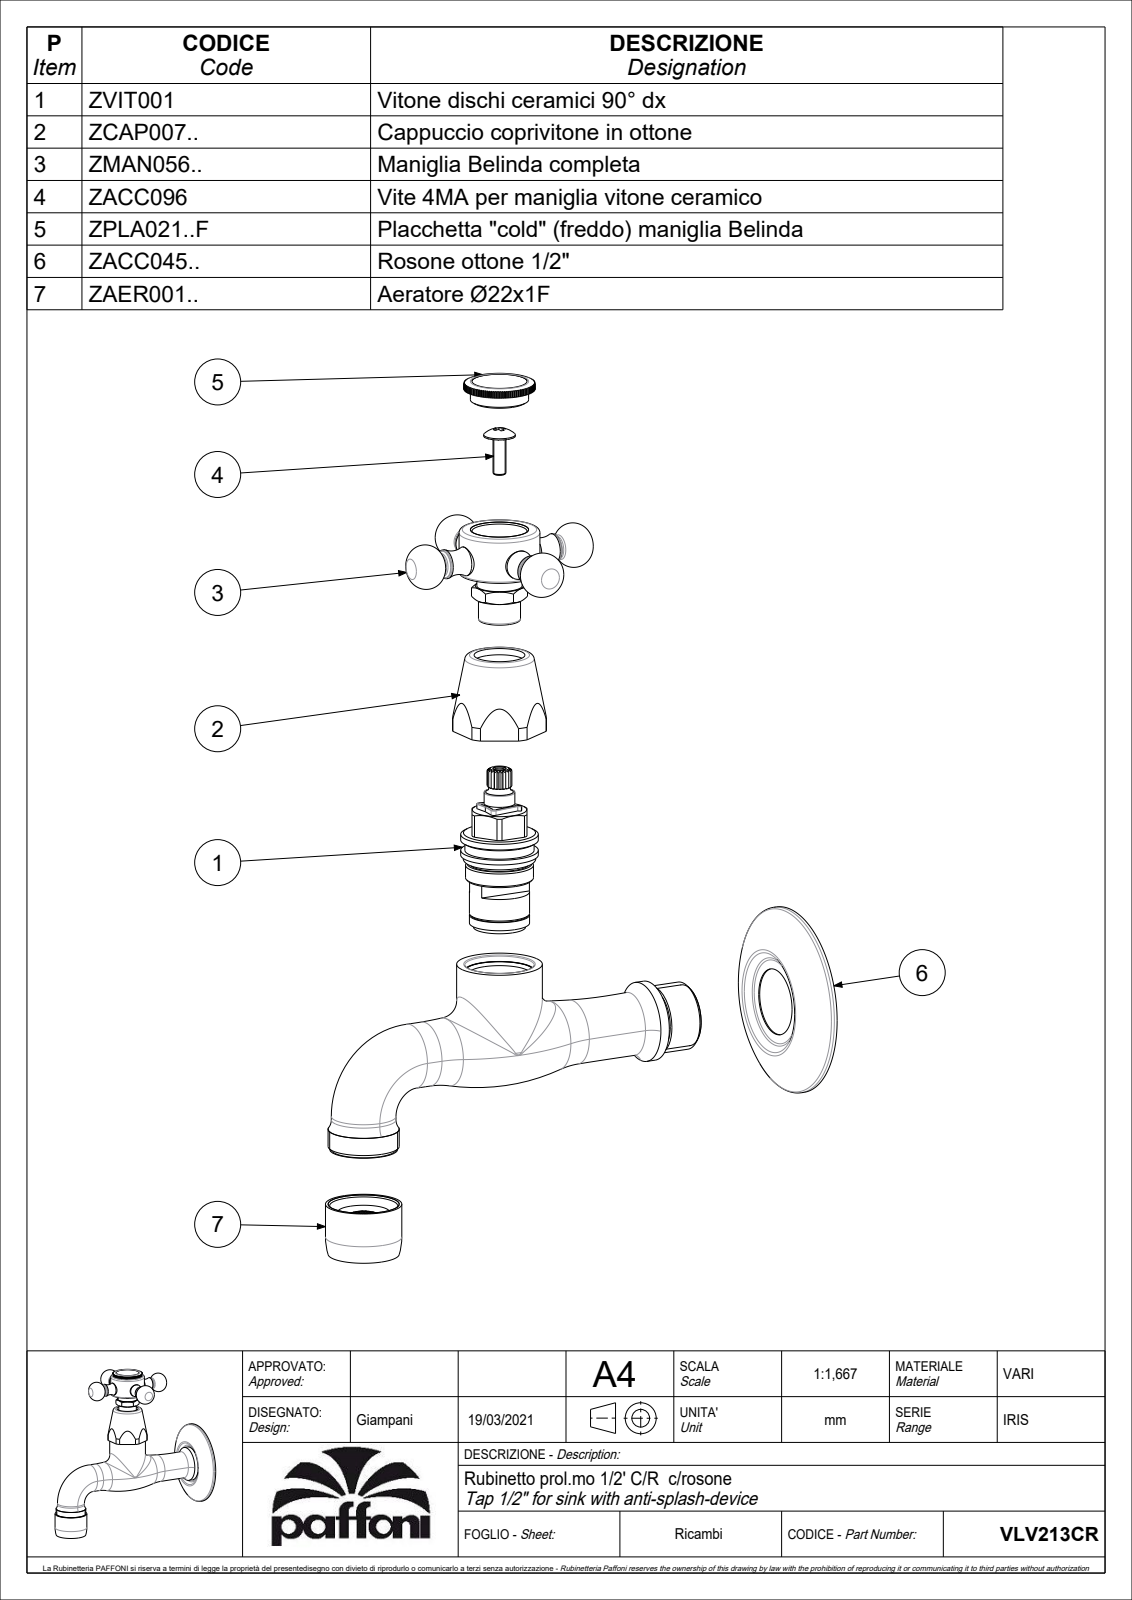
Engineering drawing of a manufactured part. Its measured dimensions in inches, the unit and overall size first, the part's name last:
Units: inches
Overall size (bounding box): 4.992 × 4.663 × 2.522
Round bosses / shafts (diameter × count): ⌀0.354 ×2, ⌀0.276 ×2, ⌀2.283 ×1, ⌀1.043 ×1, ⌀0.984 ×1, ⌀0.972 ×1, ⌀0.929 ×1, ⌀0.866 ×1
Partial cylindrical surfaces — rounded edges, fillets, slot ends (radius × count): R0.433 ×1, R0.571 ×1
Main face-to-face distances: 1.043, 0.303, 4.006, 0.226, 0.817, 3.565, 0.441, 3.557, 3.998, 2.096
Volume: 6.349 in³ · Surface area: 37.4 in²
Bodies: 1 solid, 515 faces (234 planar, 152 cylindrical, 129 other)
Part name (STEP PRODUCT): VLV213CR
STEP written by: CREO PARAMETRIC BY PTC INC, 2020044 (CONFIG_CONTROL_DESIGN)
